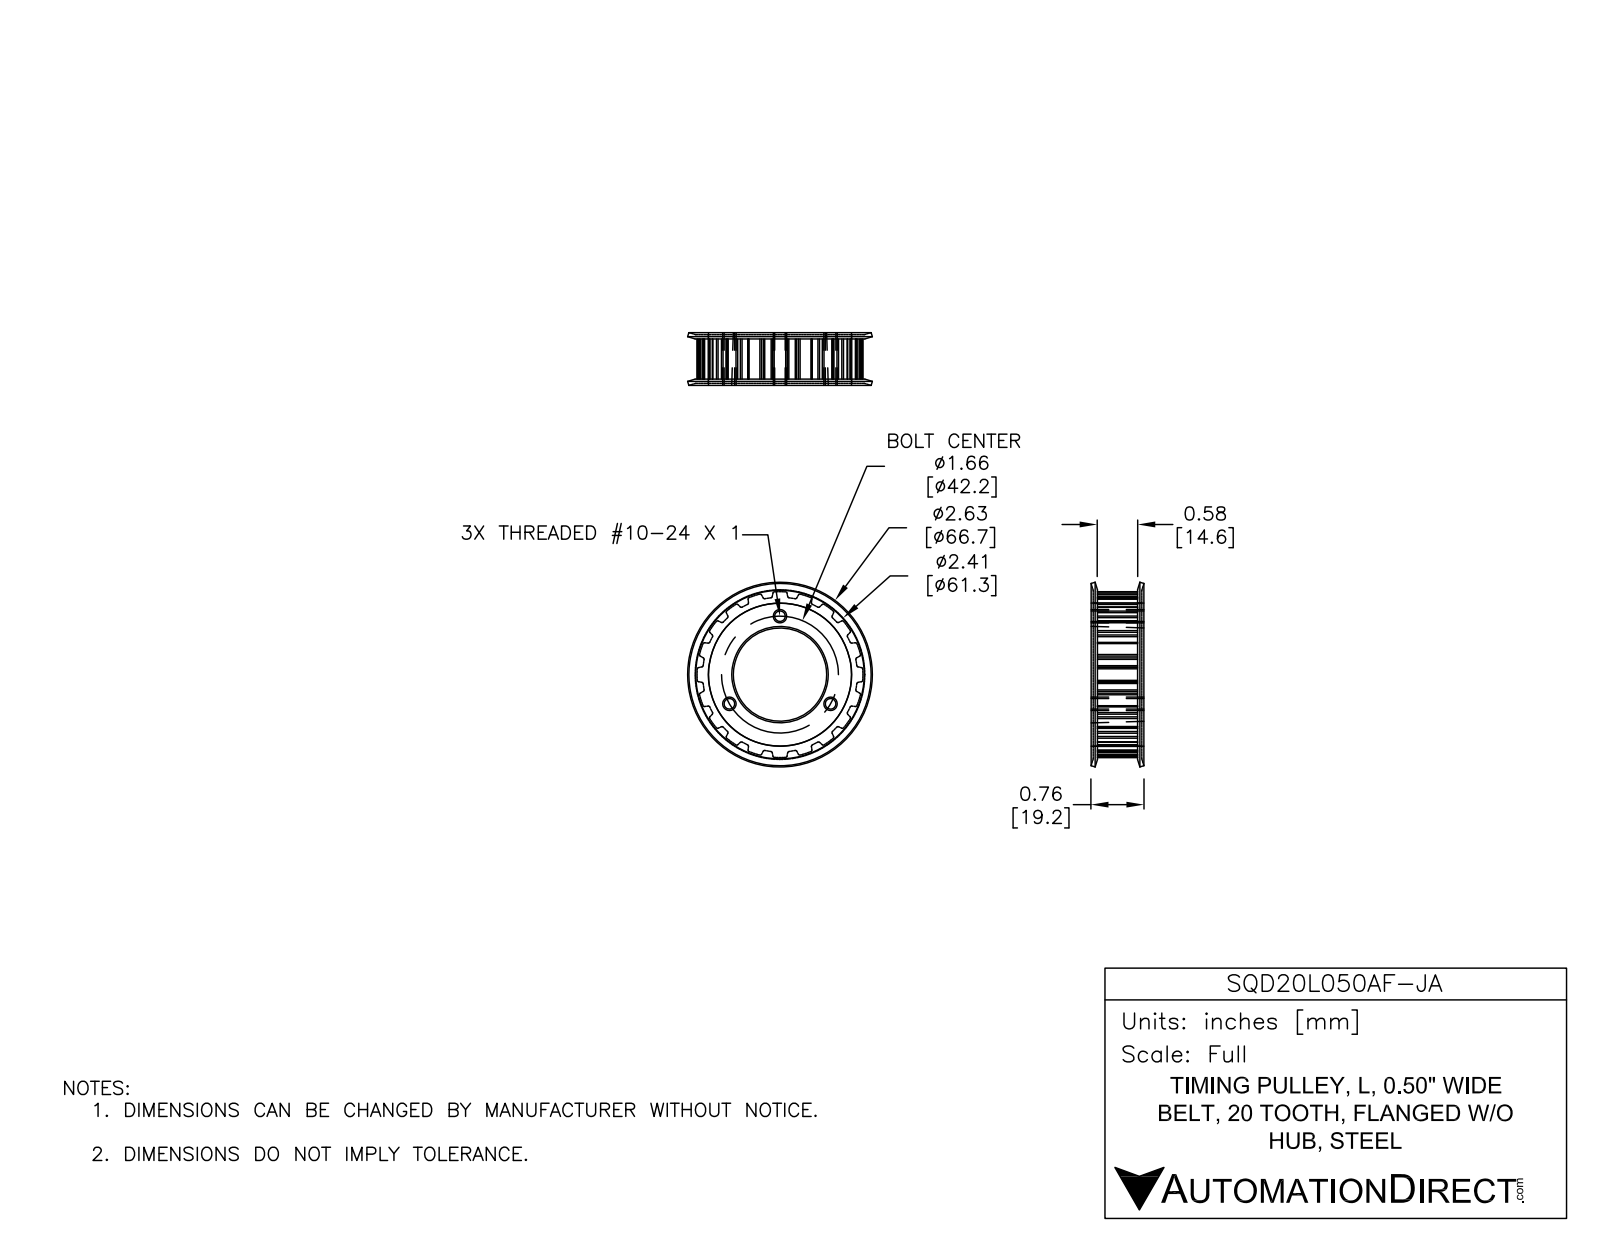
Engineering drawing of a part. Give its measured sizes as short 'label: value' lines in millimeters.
name: SQD20L050AF-JA
written by: SolidWorks 2018 (AUTOMOTIVE_DESIGN)
unit: mm
bodies: 1 solid, 225 faces (68 planar, 143 cylindrical, 14 other)
size: 66.7 × 66.7 × 19.1
volume: 34 090 mm³; area: 14 640 mm²
holes: 3× ⌀3.8, 1× ⌀51.7
bosses: 1× ⌀51.6
rounds: 80× R0.5, 1× R29.9
face distances: 0.8, 18.3, 19.1, 17.5, 16.8, 16, 1.5, 2.3, 2.3, 1.5
hole spacings: 36.5, 21.1, 21.1
